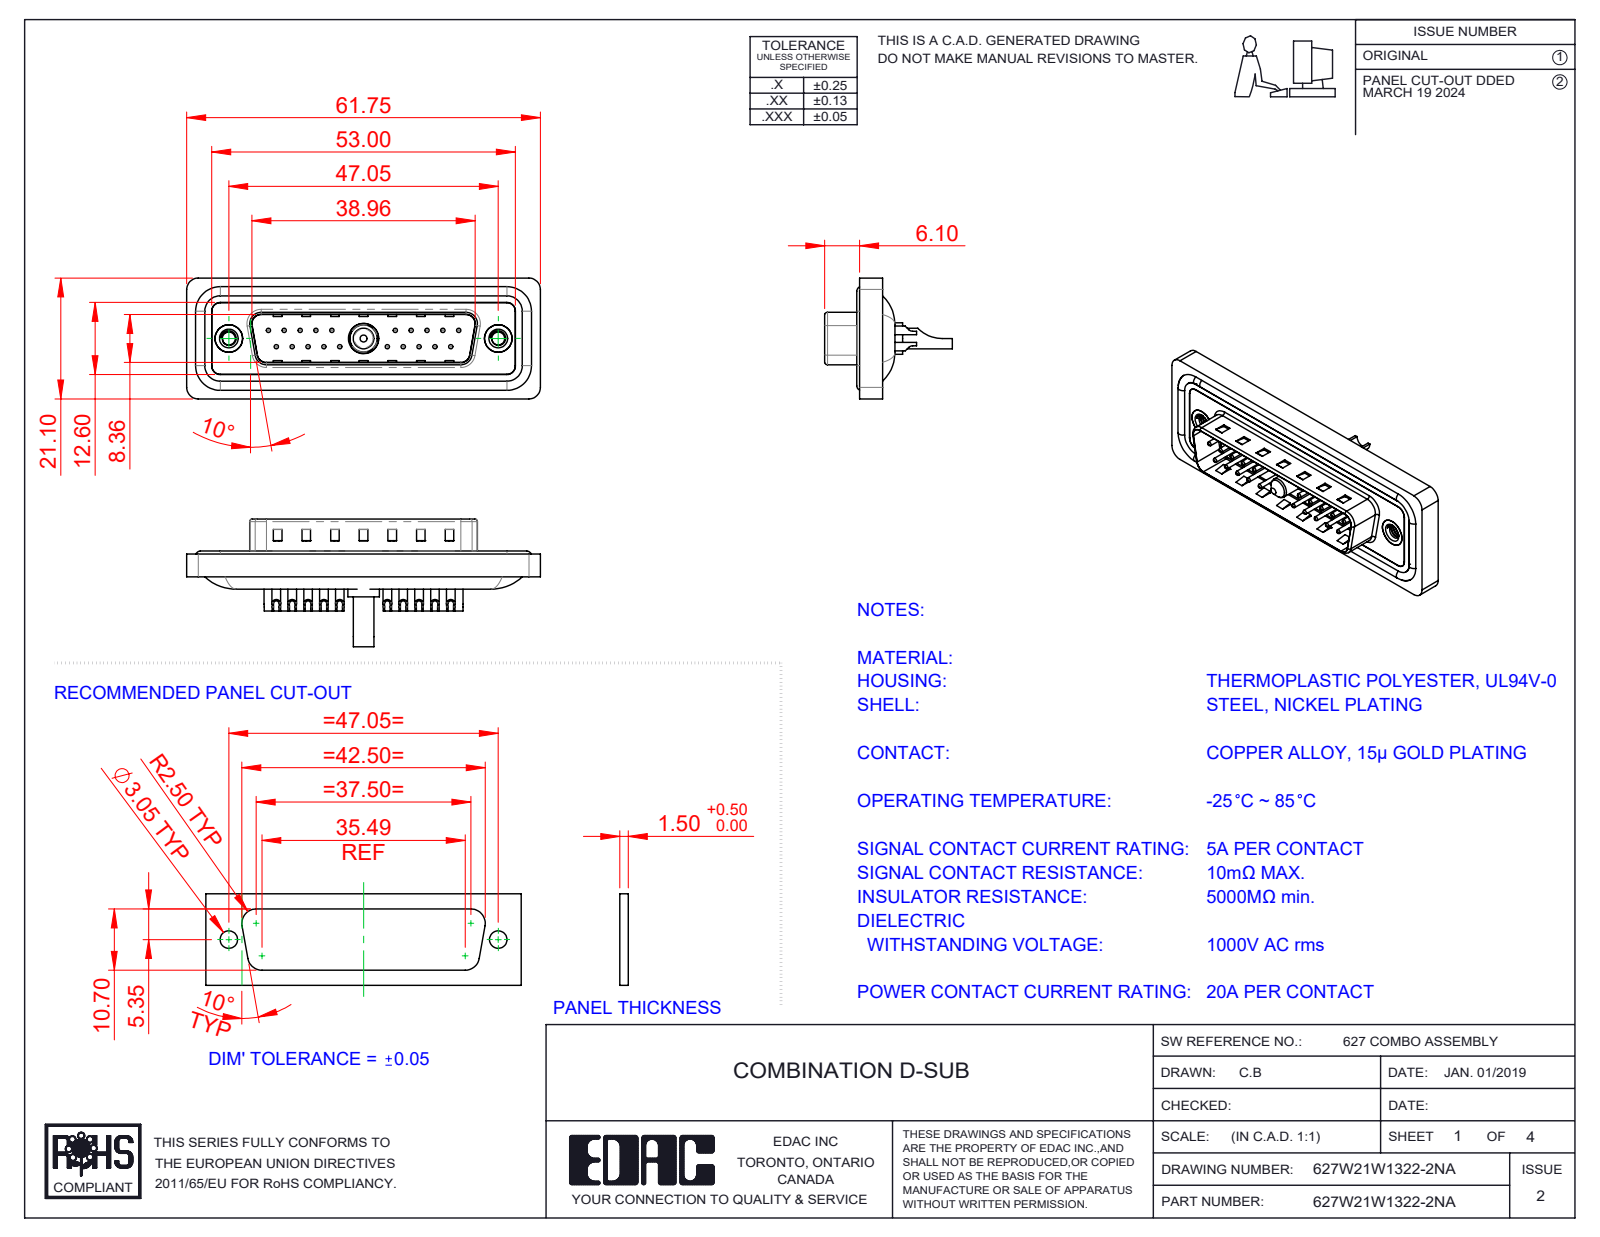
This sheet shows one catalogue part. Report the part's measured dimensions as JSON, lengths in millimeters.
{"part_name": "627Combo Housing_21W1; 627Combo Shell Rear_25 Contacts; 627Combo Threaded Rivet_A; 627Combo Contact Row 2_22 (+5 more)", "step_written_by": "SolidWorks 2023 (CONFIG_CONTROL_DESIGN)", "units": "millimeters", "bodies": {"solids": 29, "faces": 1267, "planar": 402, "cylindrical": 532, "other": 333}, "overall_size": [61.75, 22.3, 21.1], "volume_mm3": 7243, "surface_area_mm2": 12193, "round_holes": [[0.75, 20], [1, 20], [1.6, 20], [2, 20], [2.26, 2], [4, 2], [4.8, 2], [5, 2], [2.7, 1], [4.85, 1], [5.3, 1]], "round_bosses_or_shafts": [[1.5, 20], [1.6, 4], [4.9, 2], [5.5, 1], [5.2, 1], [4.75, 1], [3.75, 1], [3.6, 1]], "partial_cylinders_radius": [[1.5, 22], [2, 18], [0.5, 8], [1.6, 8], [1, 6], [0.25, 4], [0.6, 4], [0.65, 4]], "face_to_face_distances": [0.4, 1.5, 1.1, 1.6, 0.5, 3.1, 2.9, 4.1, 0.82, 9.58], "hole_center_spacings": [3.16, 2.77, 5.54, 8.31, 5.04, 19.39, 20.97, 22.16]}
